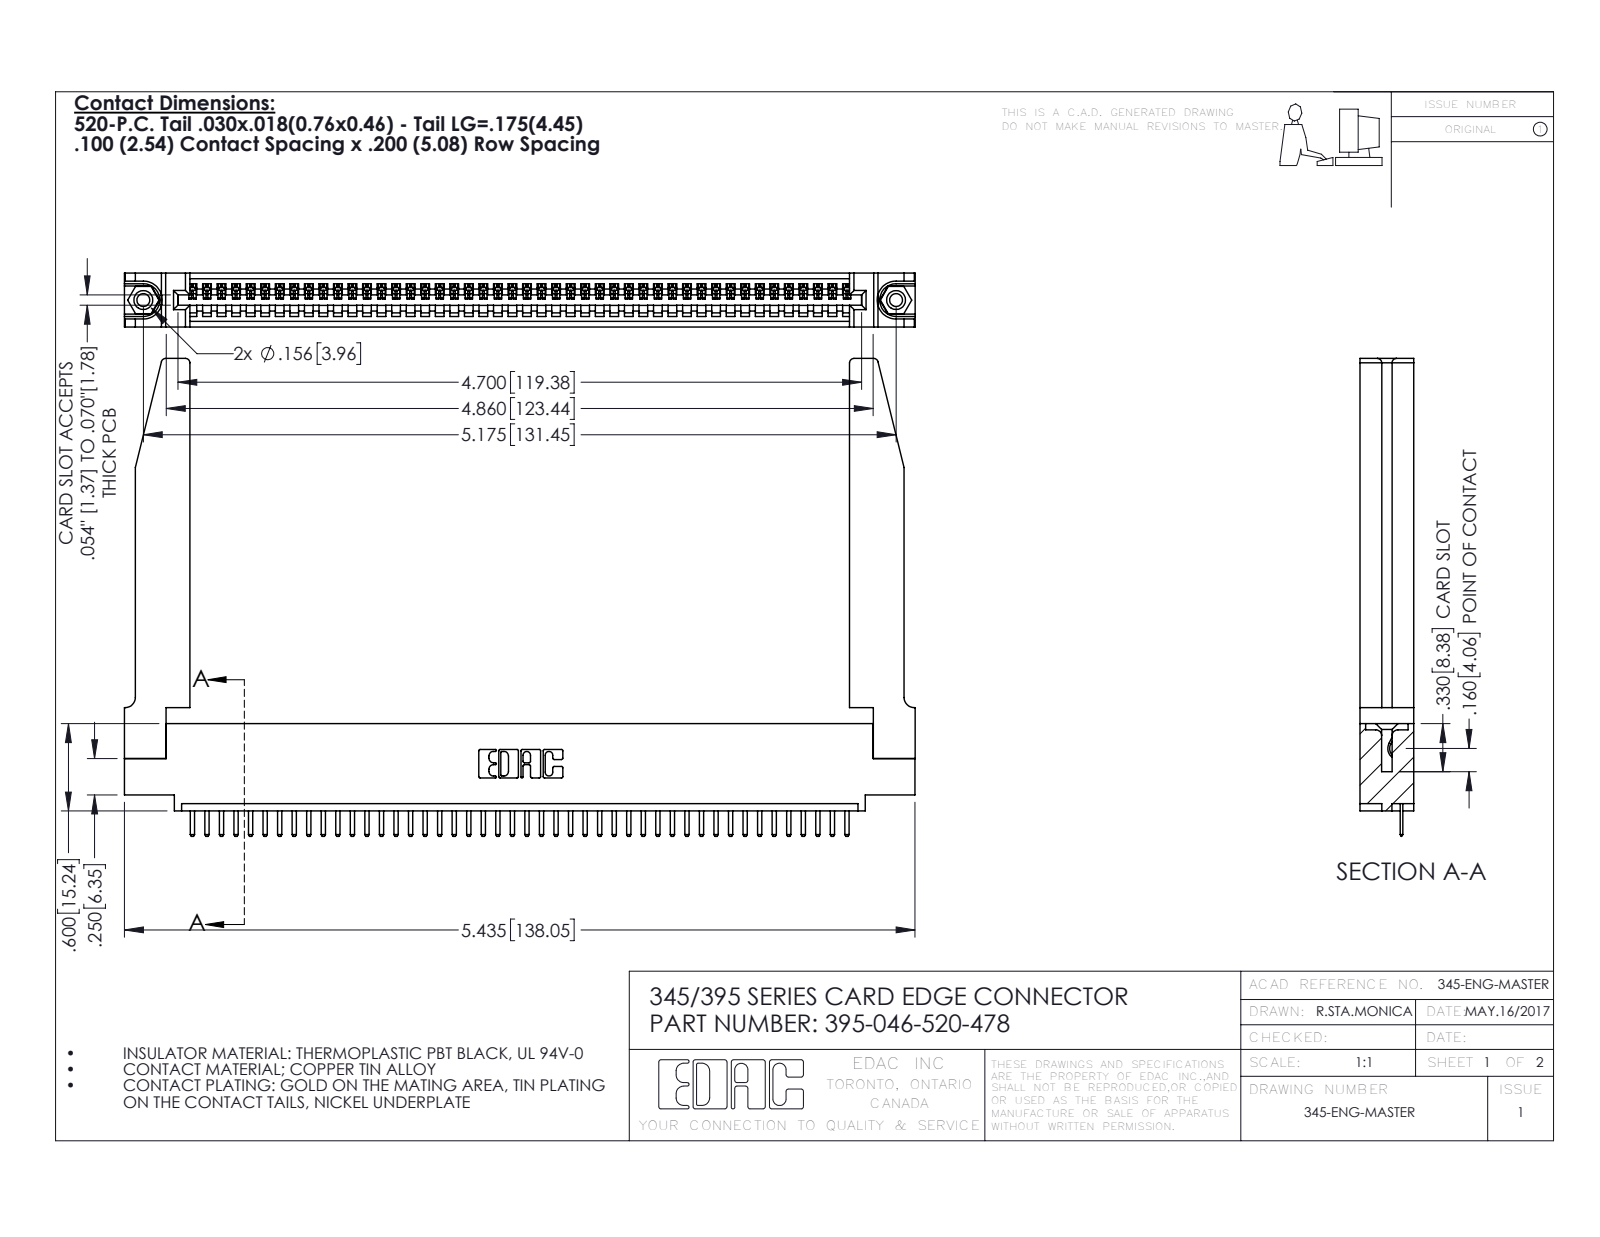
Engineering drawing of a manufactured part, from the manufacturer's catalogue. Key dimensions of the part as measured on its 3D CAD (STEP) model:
Part name (STEP PRODUCT): 345 Part_0.110 Offset - 0.156 Dia-TH; 345-292-001_345-293-120; 395-046-520-478; 345-220-078_345-220-078 (+1 more)
STEP written by: SolidWorks 2016 (CONFIG_CONTROL_DESIGN)
Units: inches
Bodies: 51 solids, 3216 faces (2158 planar, 1006 cylindrical, 52 other)
Overall size (bounding box): 5.436 × 3.285 × 0.37
Volume: 1.264 in³ · Surface area: 36.81 in²
Round holes (diameter × count): ⌀0.089 ×2, ⌀0.125 ×2, ⌀0.156 ×2, ⌀0.064 ×1
Round bosses / shafts (diameter × count): ⌀0.155 ×2
Partial cylindrical surfaces — rounded edges, fillets, slot ends (radius × count): R0.01 ×94, R0.006 ×92, R0.01 ×22, R0.03 ×8, R0.007 ×6, R0.031 ×6, R0.026 ×3, R0.031 ×2
Main face-to-face distances: 0.37, 0.072, 0.298, 0.2, 0.098, 0.272, 0.025, 0.225, 0.148, 0.15
Hole centre spacings: 0.27, 4.939, 5.175
